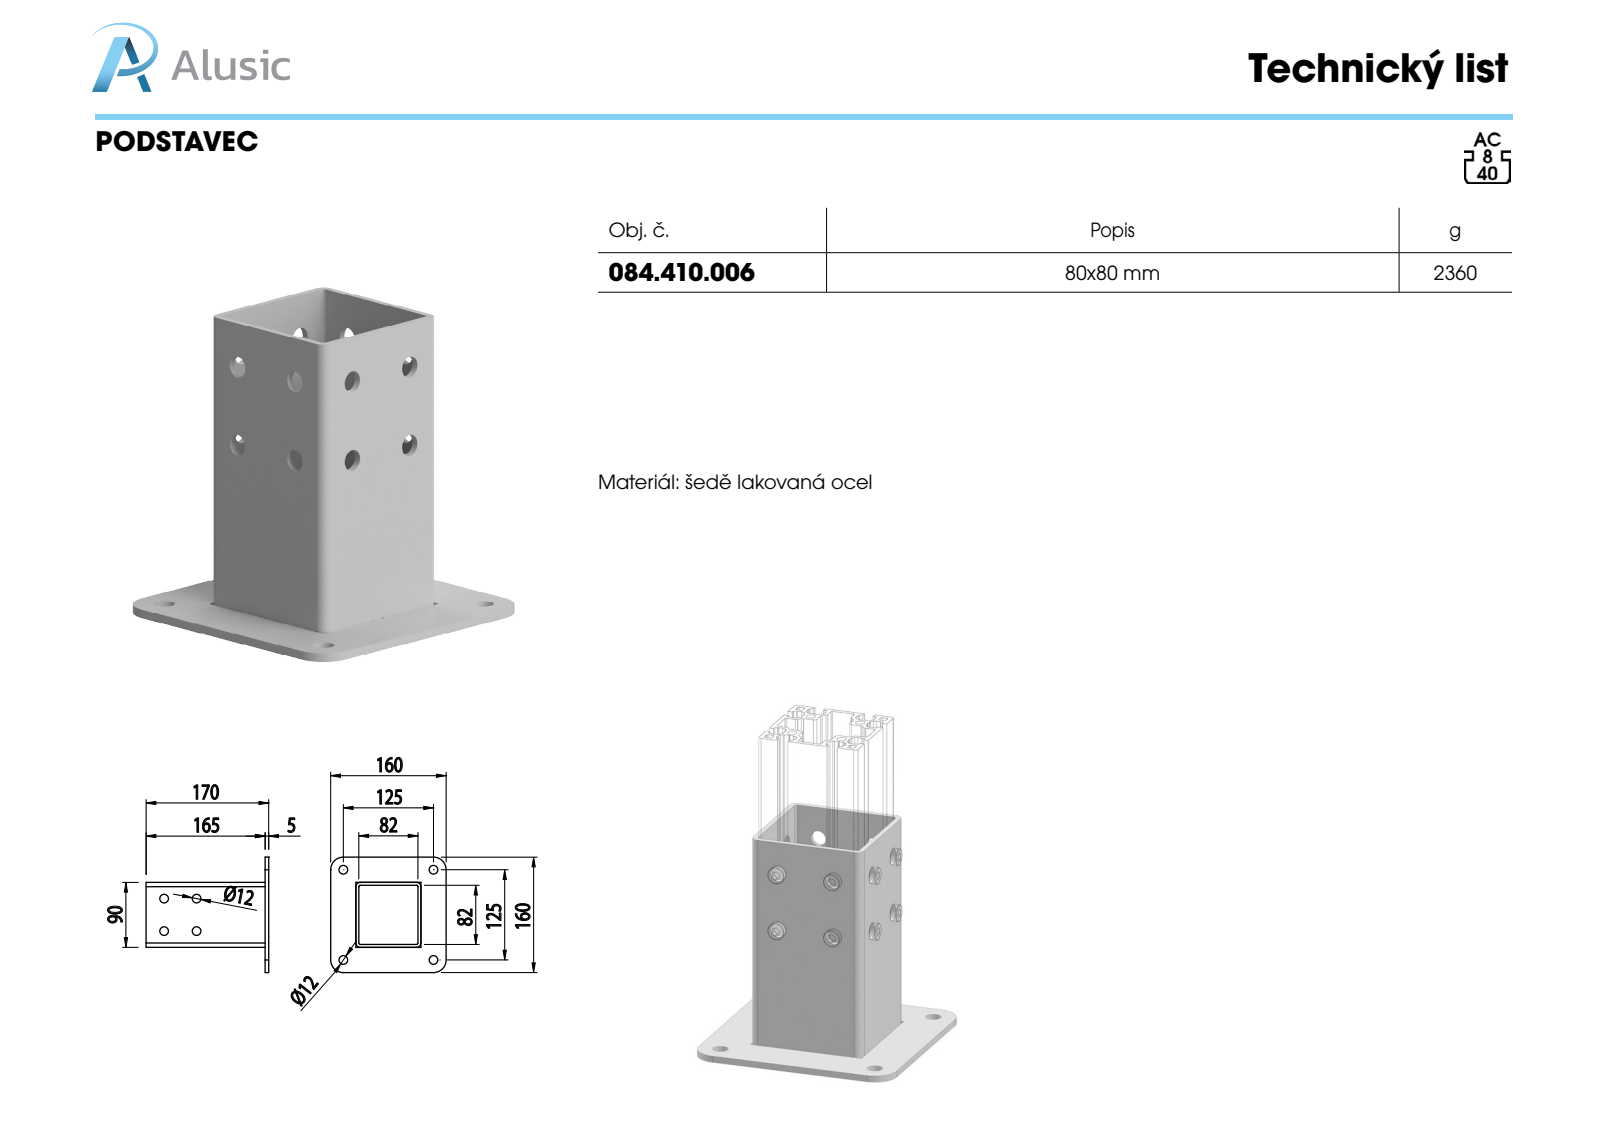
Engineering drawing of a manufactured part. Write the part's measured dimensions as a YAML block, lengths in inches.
part_name: "084.410.006"
step_written_by: "SolidWorks 2011 (CONFIG_CONTROL_DESIGN)"
units: inches
bodies: {solids: 2, faces: 72, planar: 20, cylindrical: 52, other: 0}
overall_size: [6.693, 6.299, 6.299]
volume: 18.66
surface_area: 240.6
round_holes:
  - {diameter: 0.472, count: 12}
partial_cylinders:
  - {radius: 0.079, count: 4}
  - {radius: 0.236, count: 4}
  - {radius: 0.689, count: 4}
face_to_face_distances: [0.157, 3.386, 3.543, 3.228, 0.197, 1.378, 1.535, 4.764, 4.921, 1.374]
hole_center_spacings: [1.772, 2.506, 4.921, 6.96]
